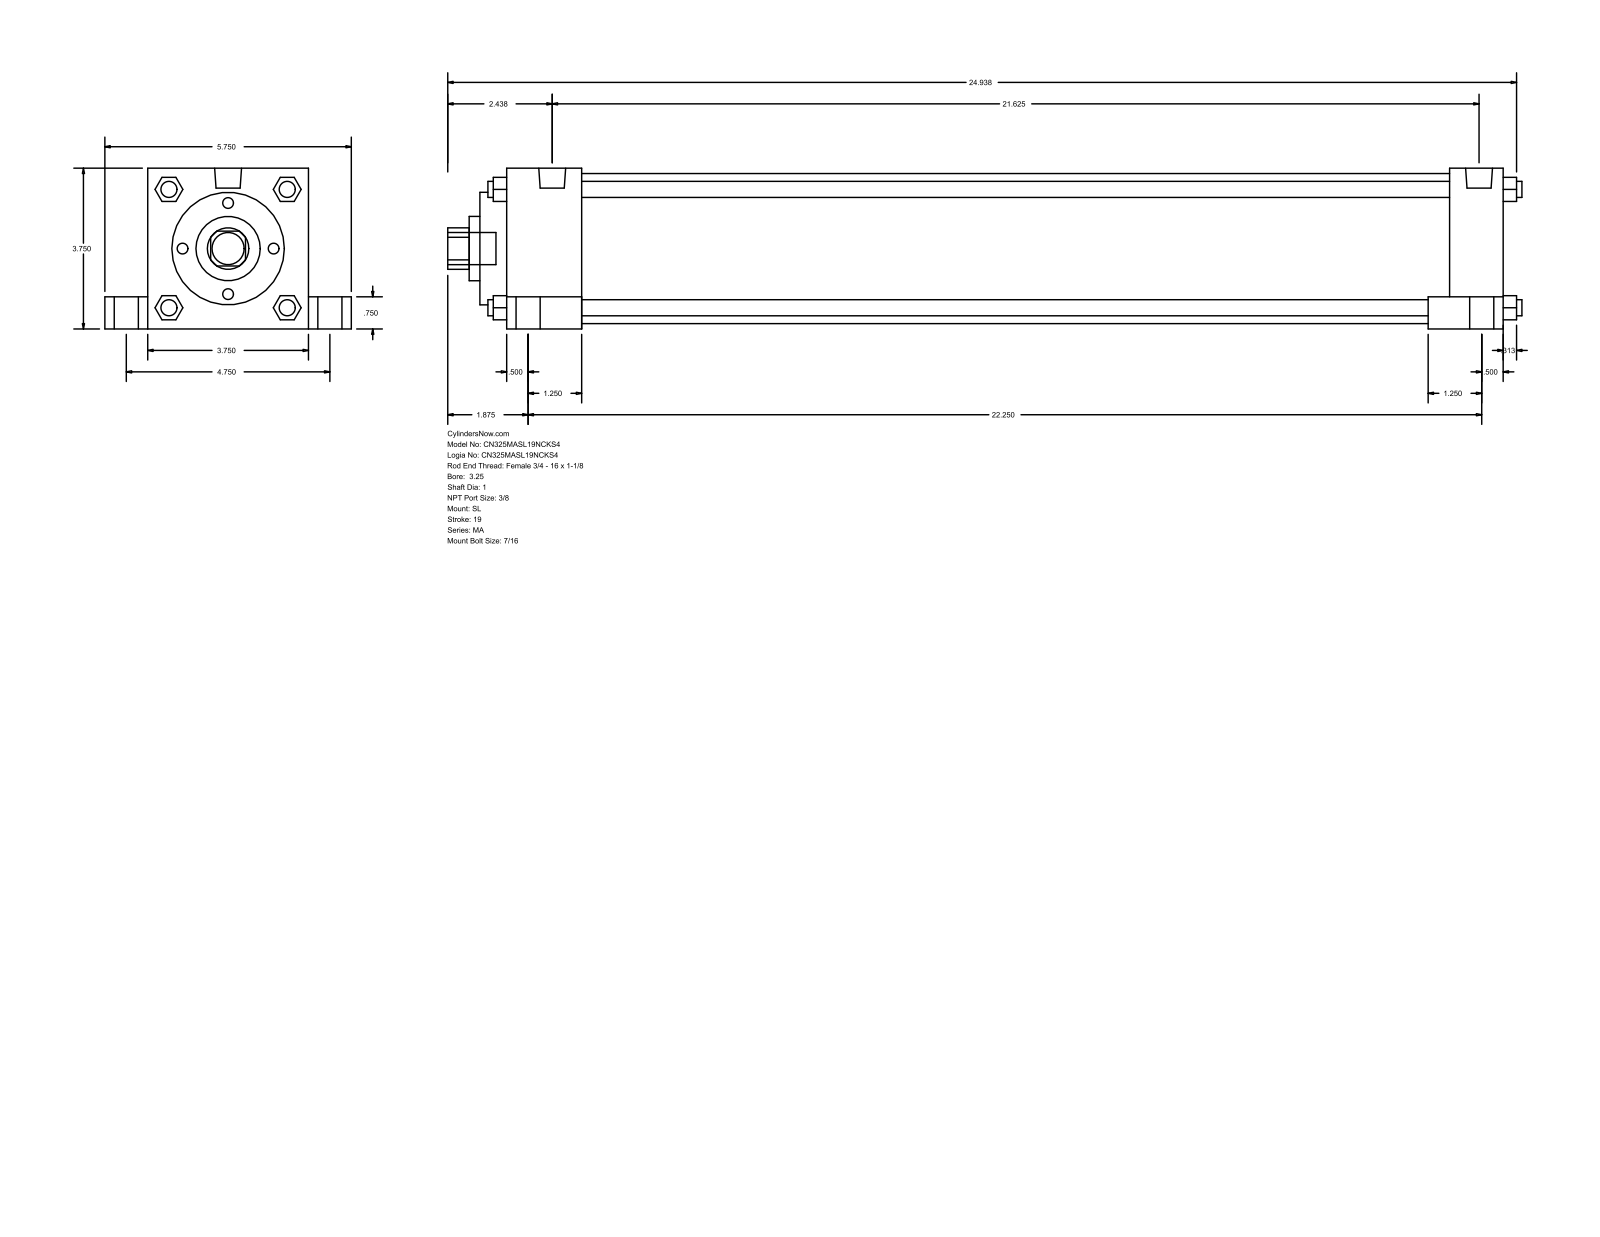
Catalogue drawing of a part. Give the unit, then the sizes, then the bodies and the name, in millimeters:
Units: millimetres
Overall size (bounding box): 636.59 × 146.05 × 95.25
Round holes (diameter × count): ⌀25.4 ×1, ⌀38.1 ×1, ⌀66.67 ×1, ⌀88.9 ×1
Round bosses / shafts (diameter × count): ⌀20.64 ×4, ⌀14.29 ×4, ⌀11.11 ×4, ⌀9.53 ×4, ⌀15.93 ×2, ⌀19.05 ×1
Partial cylindrical surfaces — rounded edges, fillets, slot ends (radius × count): R12.29 ×1
Main face-to-face distances: 95.24, 590.56, 514.35, 15.87, 25.41, 120.65, 19.05, 558.81, 31.75, 44.46
Bodies: 0 solids, 150 faces (113 planar, 37 cylindrical, 0 other)
Part name (STEP PRODUCT): MA_SL__0325_1
STEP written by: GSSL Pune (CONFIG_CONTROL_DESIGN)
